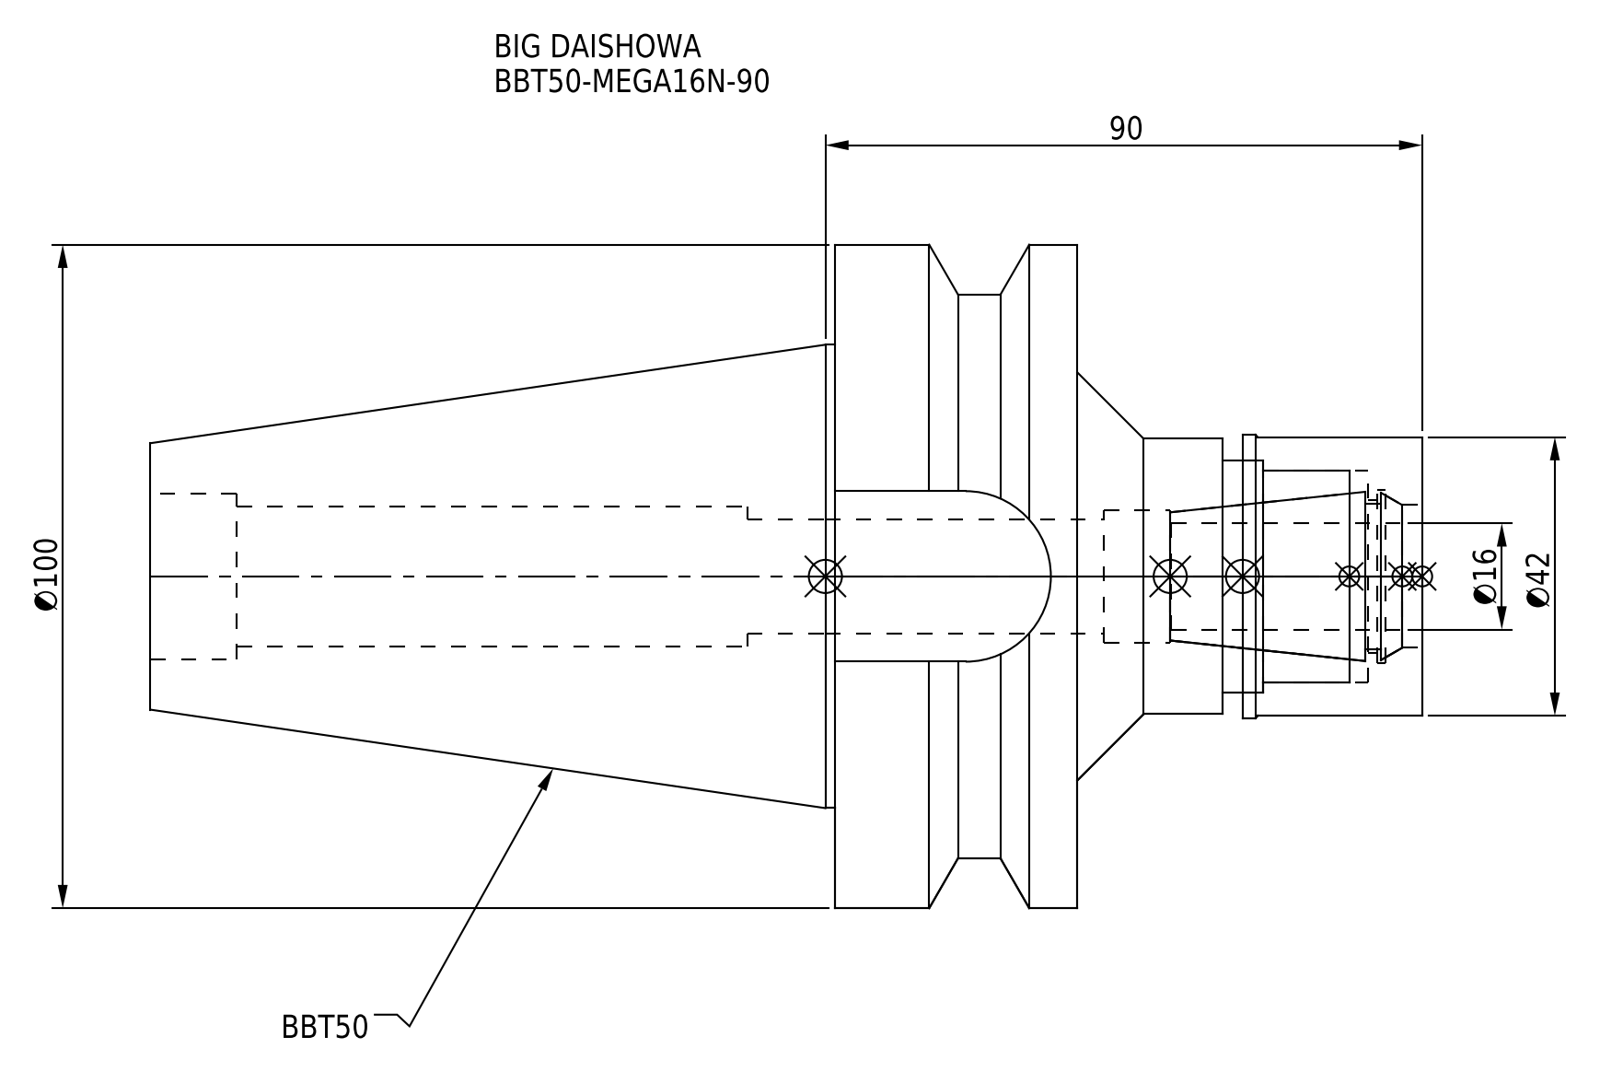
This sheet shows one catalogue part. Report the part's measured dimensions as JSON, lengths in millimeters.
{"part_name": "BBT50-MEGA16N-90_1.stp; MGN16_1.stp; BBT50-MEGA16N-90-160-FreeParts; DXF_TEMP_ASSY_ASM_4_ASM.stp (+3 more)", "step_written_by": "SolidWorks 2019 (CONFIG_CONTROL_DESIGN)", "units": "millimeters", "bodies": {"solids": 2, "faces": 76, "planar": 22, "cylindrical": 40, "other": 14}, "overall_size": [191.8, 100, 100], "volume_mm3": 511238, "surface_area_mm2": 68882, "round_holes": [[17.3, 1], [20, 1], [21.2, 1], [21.5, 1], [23, 1], [25, 1], [26, 1], [32, 1], [35, 1]], "round_bosses_or_shafts": [[100, 1], [85, 1], [69.85, 1], [42.7, 1], [42, 1], [41.5, 1]], "partial_cylinders_radius": [[12.85, 1]], "face_to_face_distances": [36.5, 52, 88.5, 21.9, 191.8, 139.8, 103.3, 70.8, 27.1, 24.9]}
